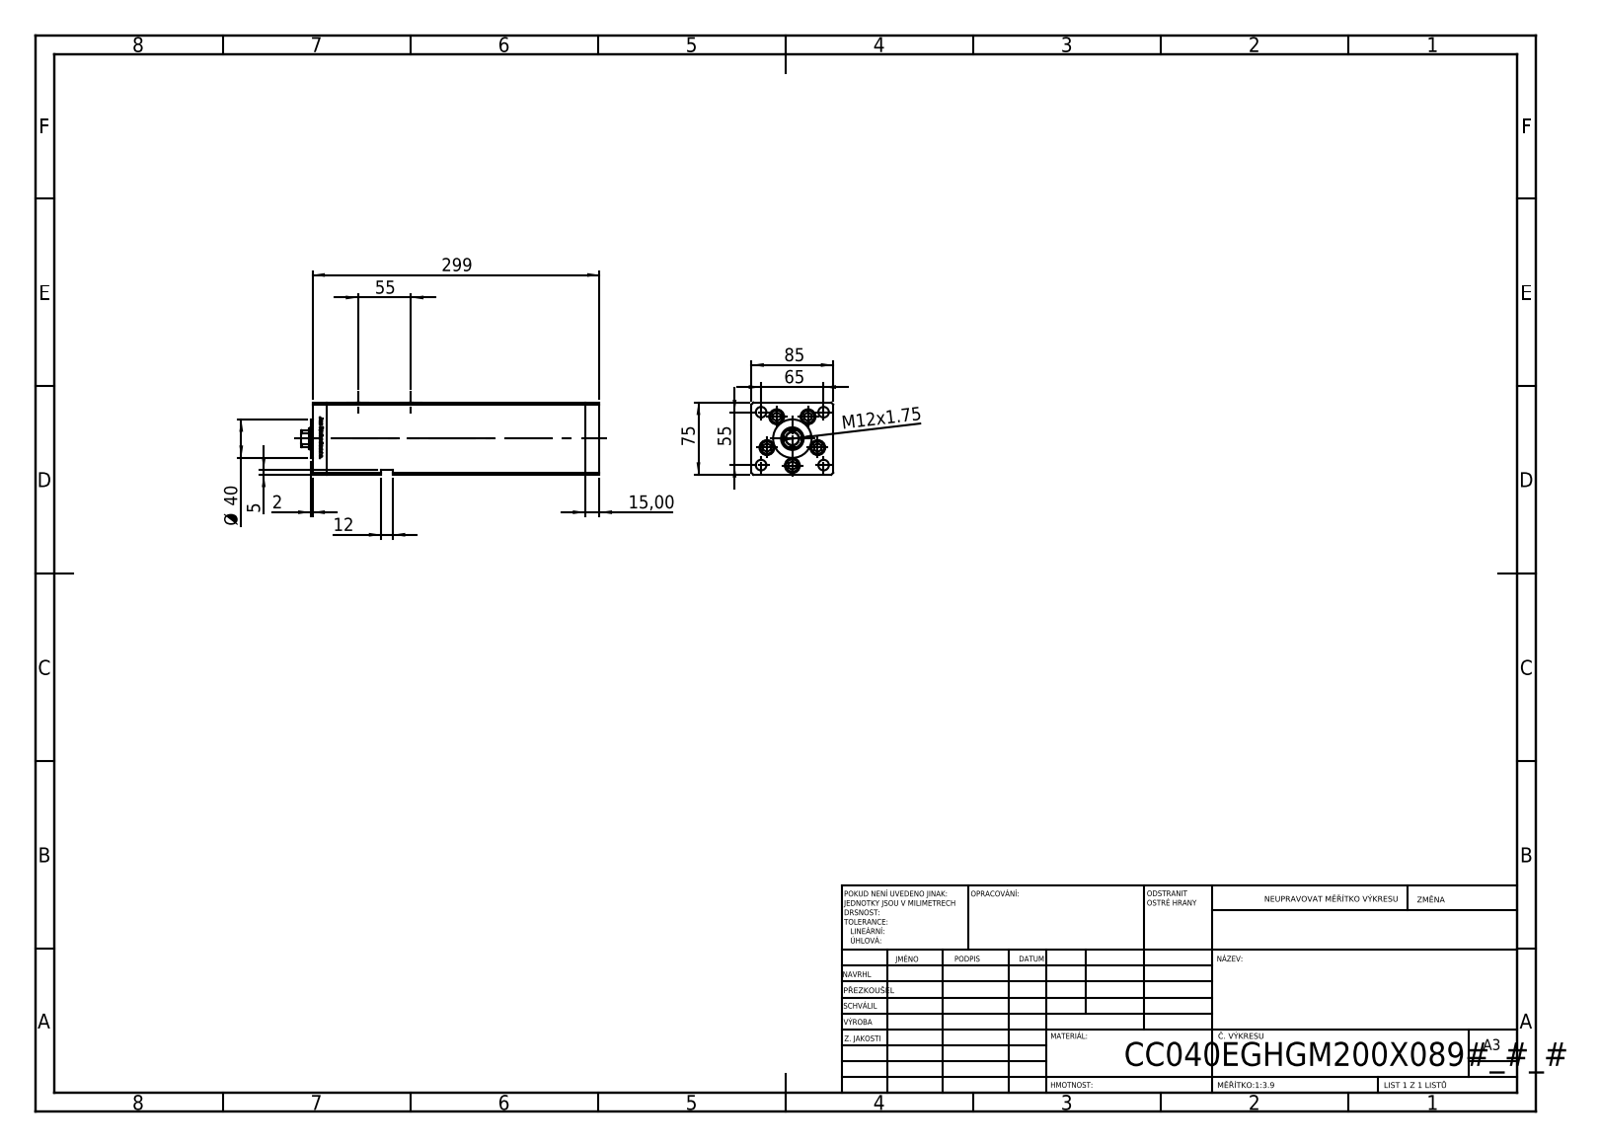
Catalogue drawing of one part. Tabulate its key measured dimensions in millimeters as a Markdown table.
| quantity | value |
| --- | --- |
| part name | V220C_E MIDDLE; V220C_FRONT_E; ALLEN BOLT; V220C_VC_E (+1 more) |
| STEP written by | SolidWorks 2019 (CONFIG_CONTROL_DESIGN) |
| units | millimeters |
| bodies | 14 solids, 1212 faces (473 planar, 165 cylindrical, 574 other) |
| overall size | 310 × 85 × 75 |
| volume | 1 606 000 mm³ |
| surface area | 236 250 mm² |
| round holes (diameter × count) | 11 × 9, 15.5 × 5, 10.5 × 4, 16.5 × 4, 2 × 2, 13.16 × 2, 13.5 × 1, 22 × 1, 23.5 × 1 |
| round bosses / shafts (diameter × count) | 14.5 × 5, 8 × 5, 40 × 1 |
| partial cylindrical surfaces (radius × count) | 0.93 × 2, 10.5 × 1 |
| main face-to-face distances | 85, 75, 15, 268.5, 283.5, 10.5, 68.5, 298.5, 64.5, 31.25 |
| hole center spacings | 28, 42.57, 55, 65, 85.15, 16.86, 19.17, 32.33 |
